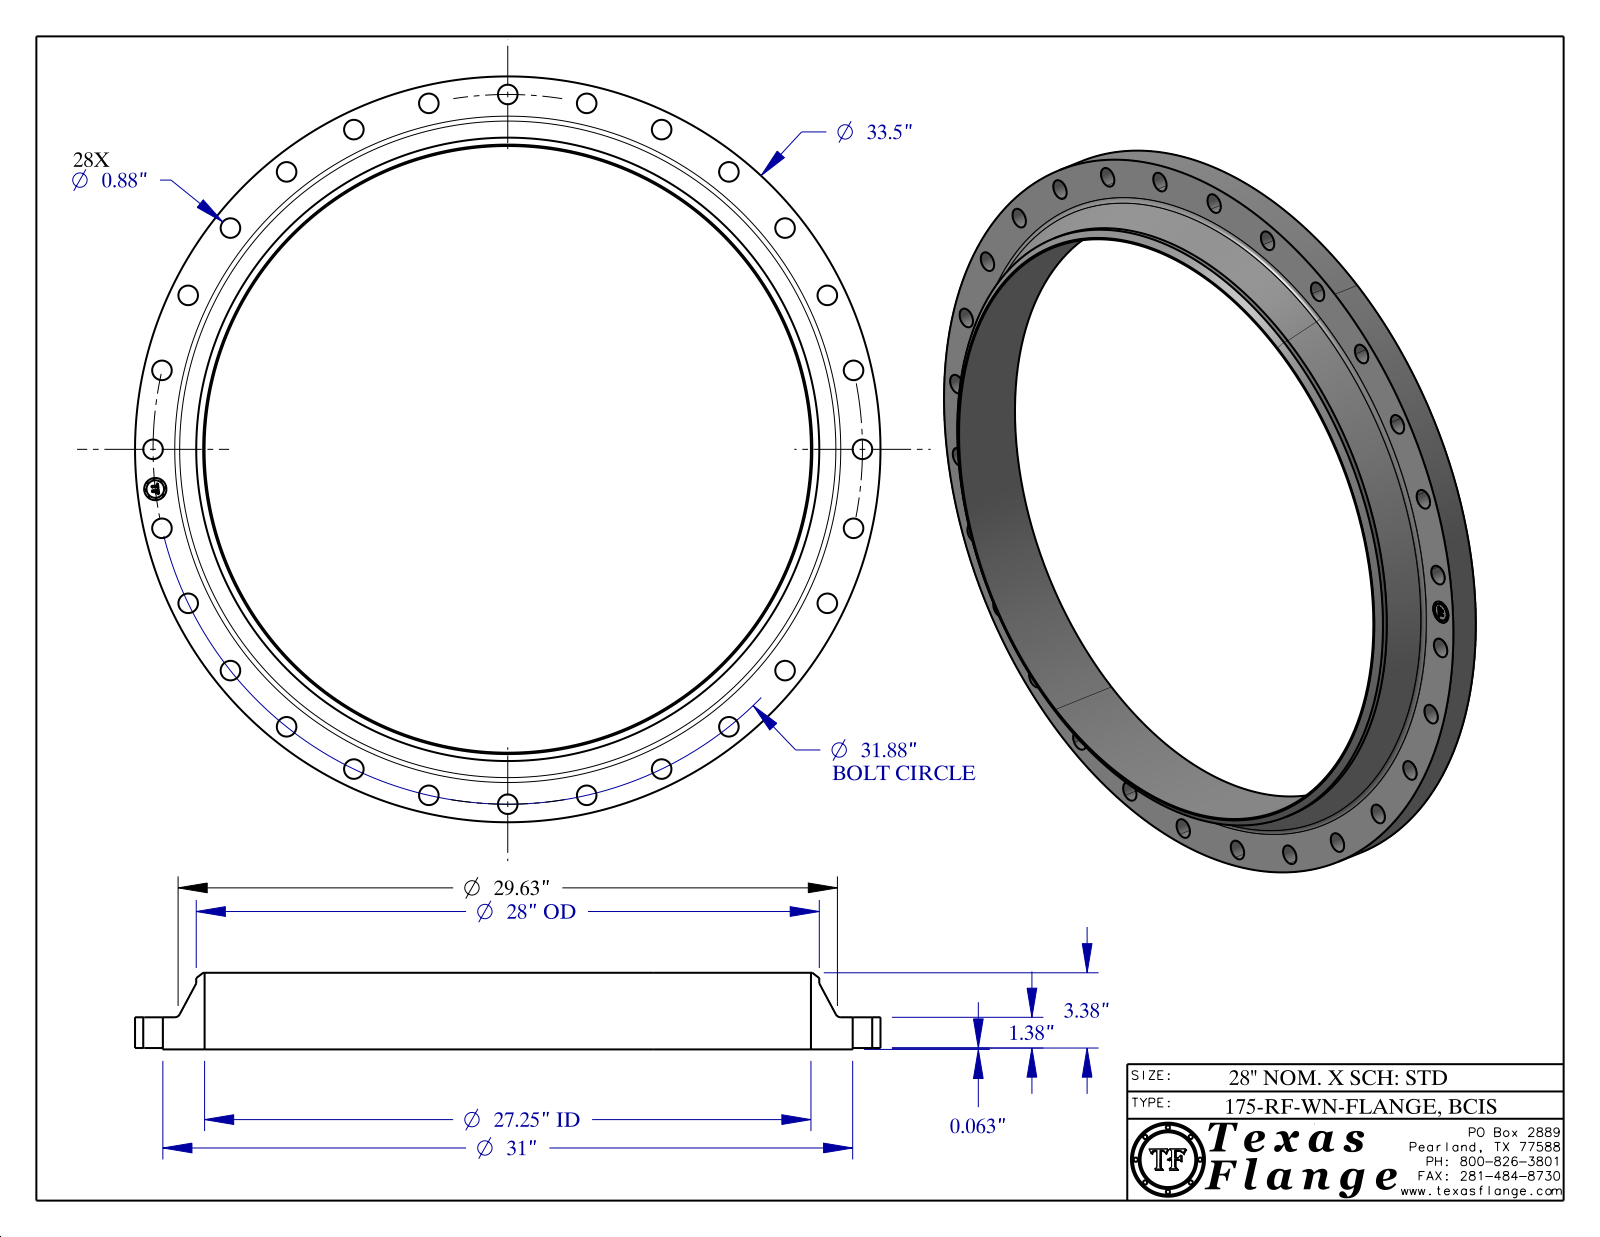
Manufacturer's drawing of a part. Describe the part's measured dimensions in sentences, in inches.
The part is named "175-RF-WN, BCIS". Its 3-D file was written by "CATIA V5 STEP AP214 (AUTOMOTIVE_DESIGN)". It is 1 solid with 459 faces: 369 planar, 84 cylindrical and 6 other. Overall it measures 33.5 by 33.5 by 3.443 inches. Its volume is 516.6 cubic inches and its surface area 1 223 square inches. Round holes: 28 of diameter 0.88, 1 of diameter 1, 1 of diameter 27.25. Round bosses or shafts: 8 of diameter 0.061, 1 of diameter 33.5, 1 of diameter 31, 1 of diameter 28, 1 of diameter 0.788. The main face-to-face distances are 1.443, 0.063, 1.38, 3.443, 3.38, 2, 0.015, 1.428, 1.365, 2.015. The hole center spacings are 30.091, 19.877, 24.925, 10.529, 13.832, 31.68, 3.57, 7.094.
